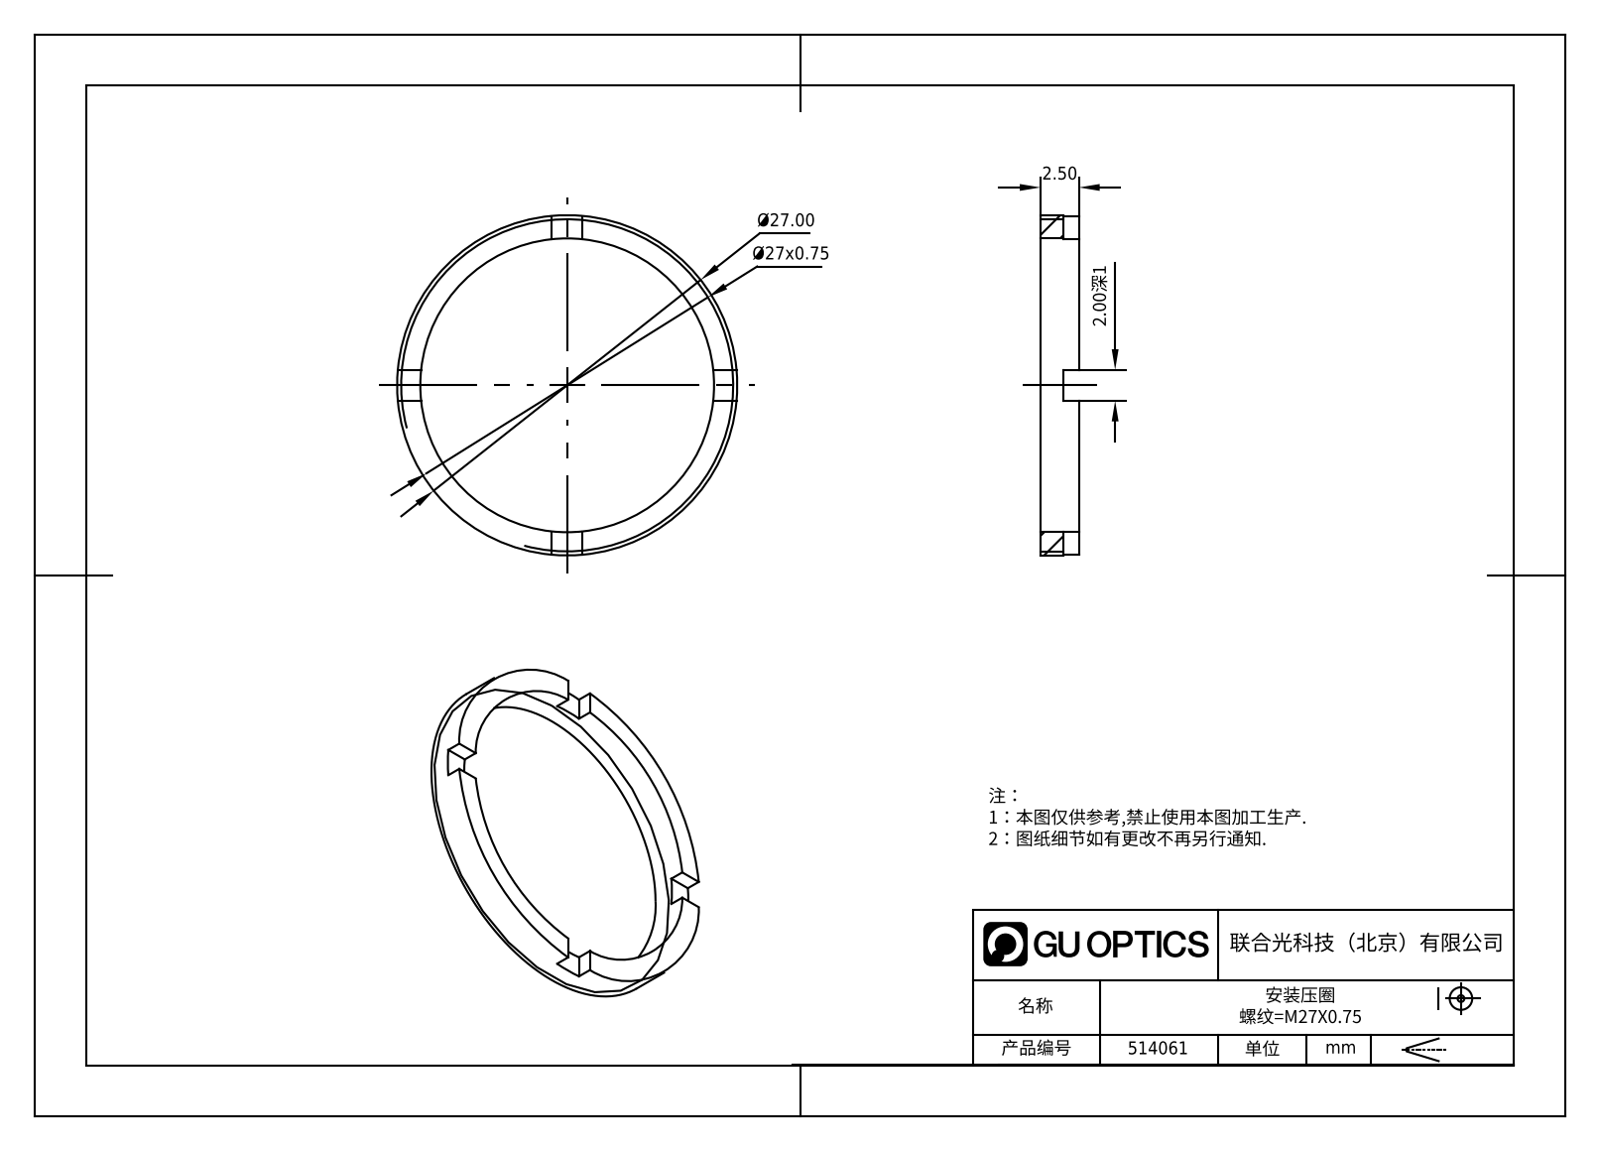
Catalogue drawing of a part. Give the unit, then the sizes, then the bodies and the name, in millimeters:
Units: millimetres
Overall size (bounding box): 27 × 27 × 2.5
Round holes (diameter × count): ⌀24 ×1
Round bosses / shafts (diameter × count): ⌀27 ×1
Main face-to-face distances: 2.5, 1.5, 1, 2
Volume: 288 mm³ · Surface area: 637 mm²
Bodies: 1 solid, 21 faces (17 planar, 4 cylindrical, 0 other)
Part name (STEP PRODUCT): 514061
STEP written by: SolidWorks 2020 (CONFIG_CONTROL_DESIGN)
